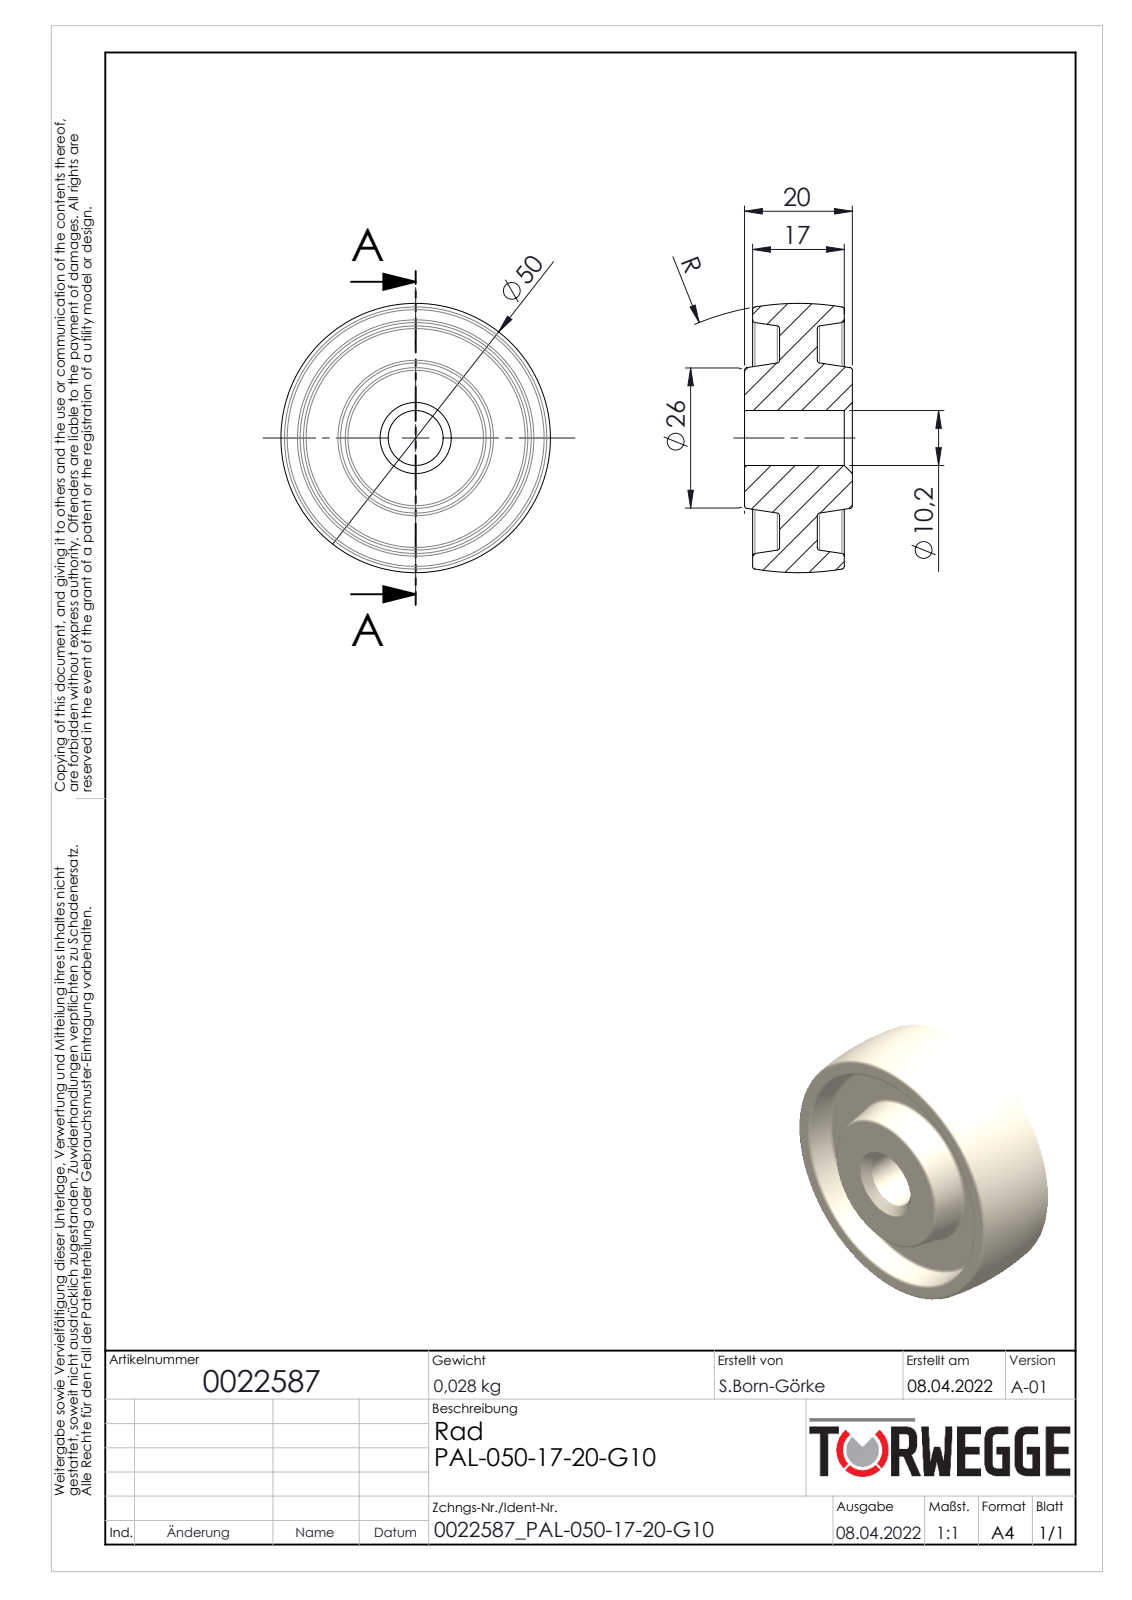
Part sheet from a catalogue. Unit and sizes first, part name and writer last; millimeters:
Units: millimetres
Overall size (bounding box): 50 × 50 × 20
Round holes (diameter × count): ⌀10.2 ×1
Main face-to-face distances: 6.5, 13.5, 7, 1.5, 18.5, 5, 12, 20, 17
Volume: 24 451 mm³ · Surface area: 8 719 mm²
Bodies: 1 solid, 42 faces (6 planar, 2 cylindrical, 34 other)
Part name (STEP PRODUCT): 0022587
STEP written by: SolidWorks 2020 (AUTOMOTIVE_DESIGN)
